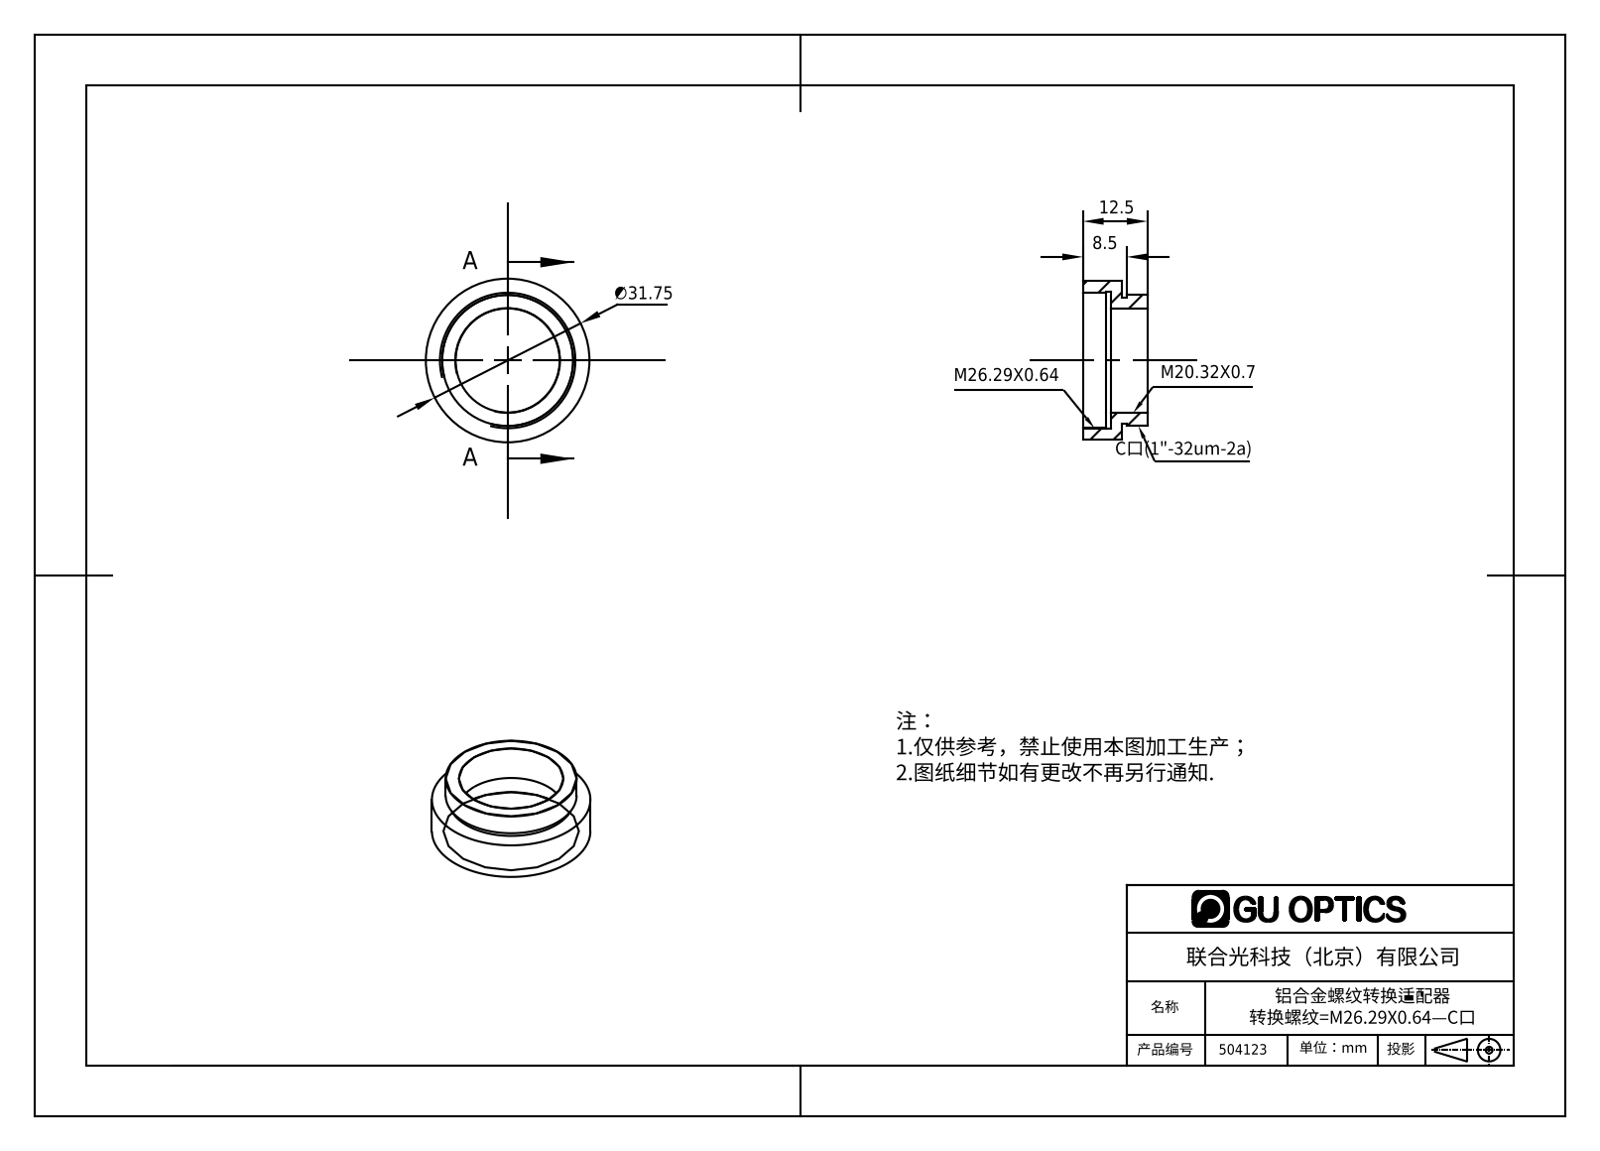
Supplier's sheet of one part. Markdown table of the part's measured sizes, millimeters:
| quantity | value |
| --- | --- |
| part name | 504123 |
| STEP written by | SolidWorks 2016 (AUTOMOTIVE_DESIGN) |
| units | millimeters |
| bodies | 1 solid, 18 faces (6 planar, 12 cylindrical, 0 other) |
| overall size | 31.75 × 31.75 × 12.5 |
| volume | 3 215 mm³ |
| surface area | 3 089 mm² |
| round holes (diameter × count) | 20.2 × 1, 26.2 × 1, 26.5 × 1 |
| round bosses / shafts (diameter × count) | 31.75 × 1, 25.42 × 1, 24.4 × 1 |
| main face-to-face distances | 7.5, 5.5, 2, 12.5, 7, 5, 1, 3, 4, 8.5 |
